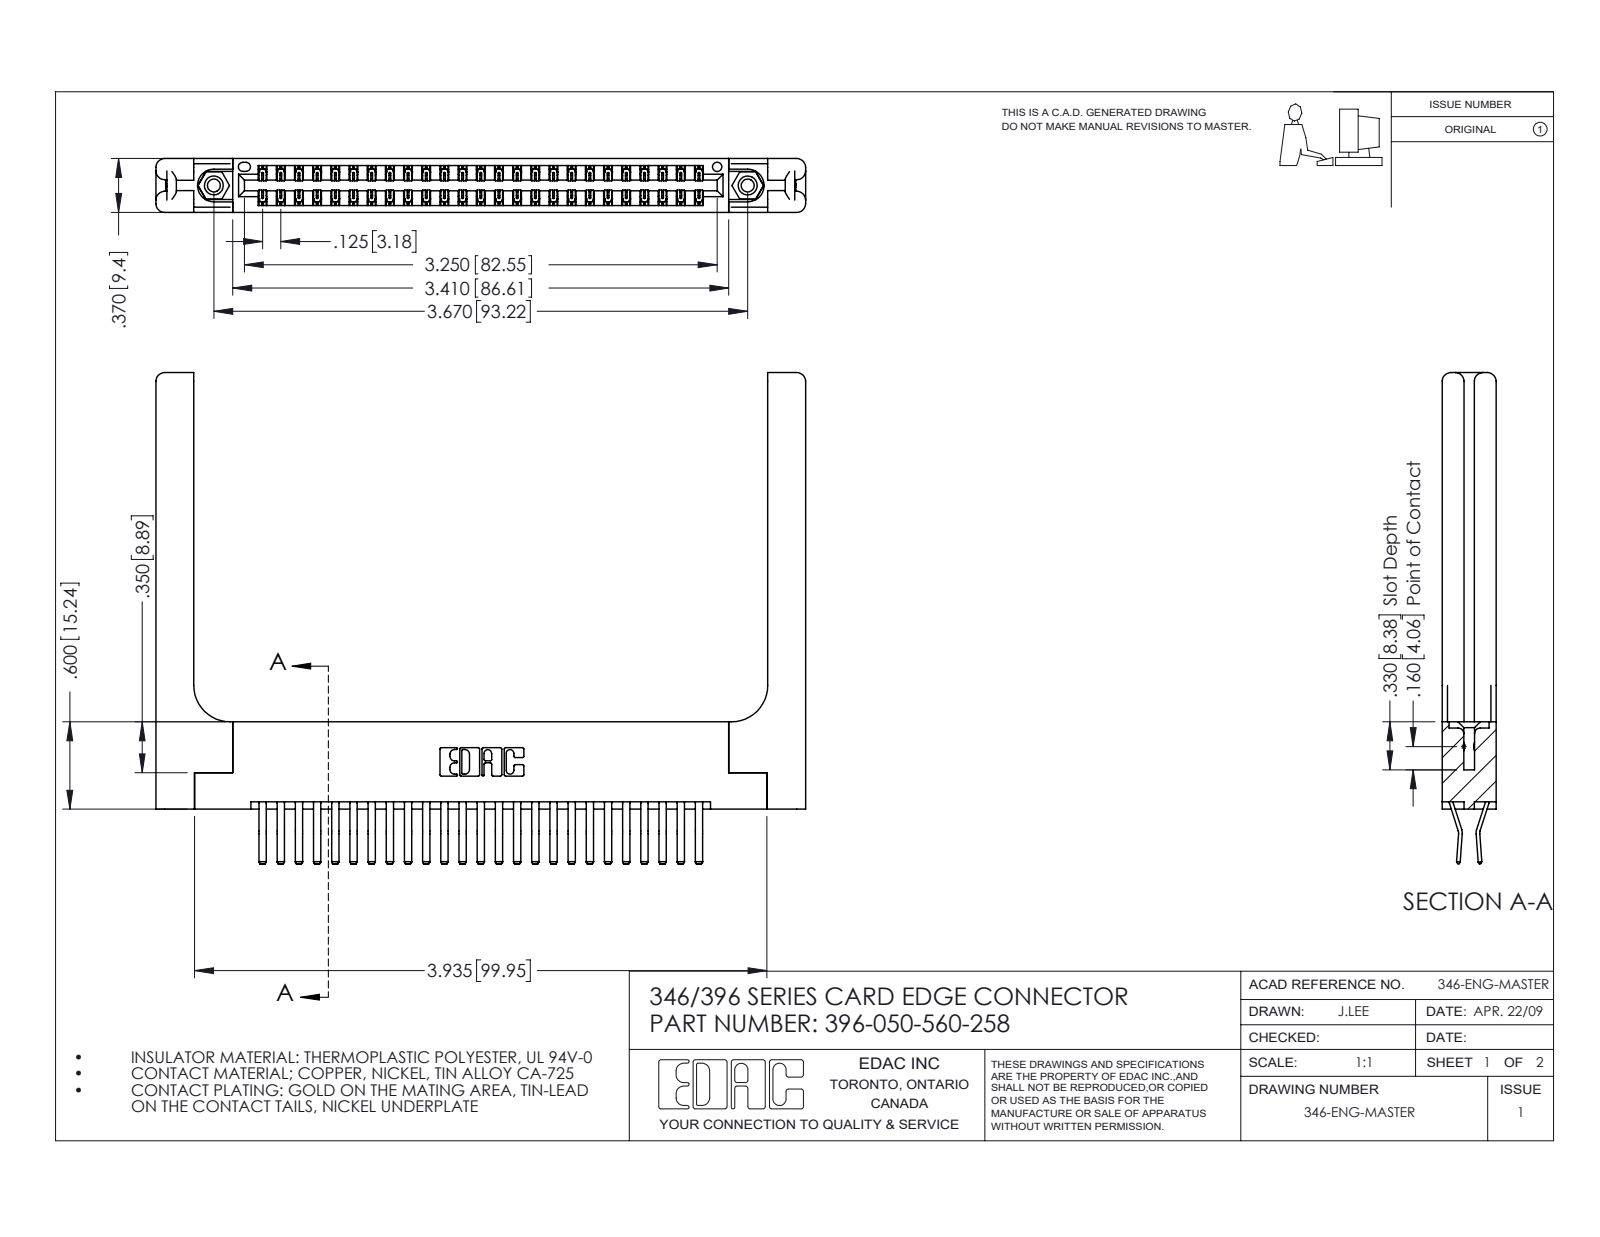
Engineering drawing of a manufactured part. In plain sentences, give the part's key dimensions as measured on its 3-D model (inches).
The part is named "345-292-001_560 Tail; 346 Part_Flush Mounting Lugs - 0.156 Dia-TH; 346-220-058_345-220-058; 345-250-001_345-250-001-102 (+1 more)". Its 3-D file was written by "SolidWorks 2016 (CONFIG_CONTROL_DESIGN)". It is 55 solids with 3078 faces: 1974 planar, 1044 cylindrical and 60 other. Overall it measures 4.466 by 3.375 by 0.37 inches. Its volume is 1.144 cubic inches and its surface area 32.63 square inches. Round holes: 2 of diameter 0.089, 2 of diameter 0.125, 2 of diameter 0.156, 1 of diameter 0.064. Round bosses or shafts: 2 of diameter 0.155. Partial cylindrical surfaces (rounded edges, fillets, slot ends): 75 of radius 0.006, 22 of radius 0.01, 16 of radius 0.06, 6 of radius 0.007, 6 of radius 0.031, 3 of radius 0.026, 2 of radius 0.01, 2 of radius 0.014. The main face-to-face distances are 0.37, 0.072, 0.048, 0.322, 0.148, 0.15, 0.025, 0.25, 0.298, 0.275. The hole center spacings are 0.246, 3.462, 3.67.
